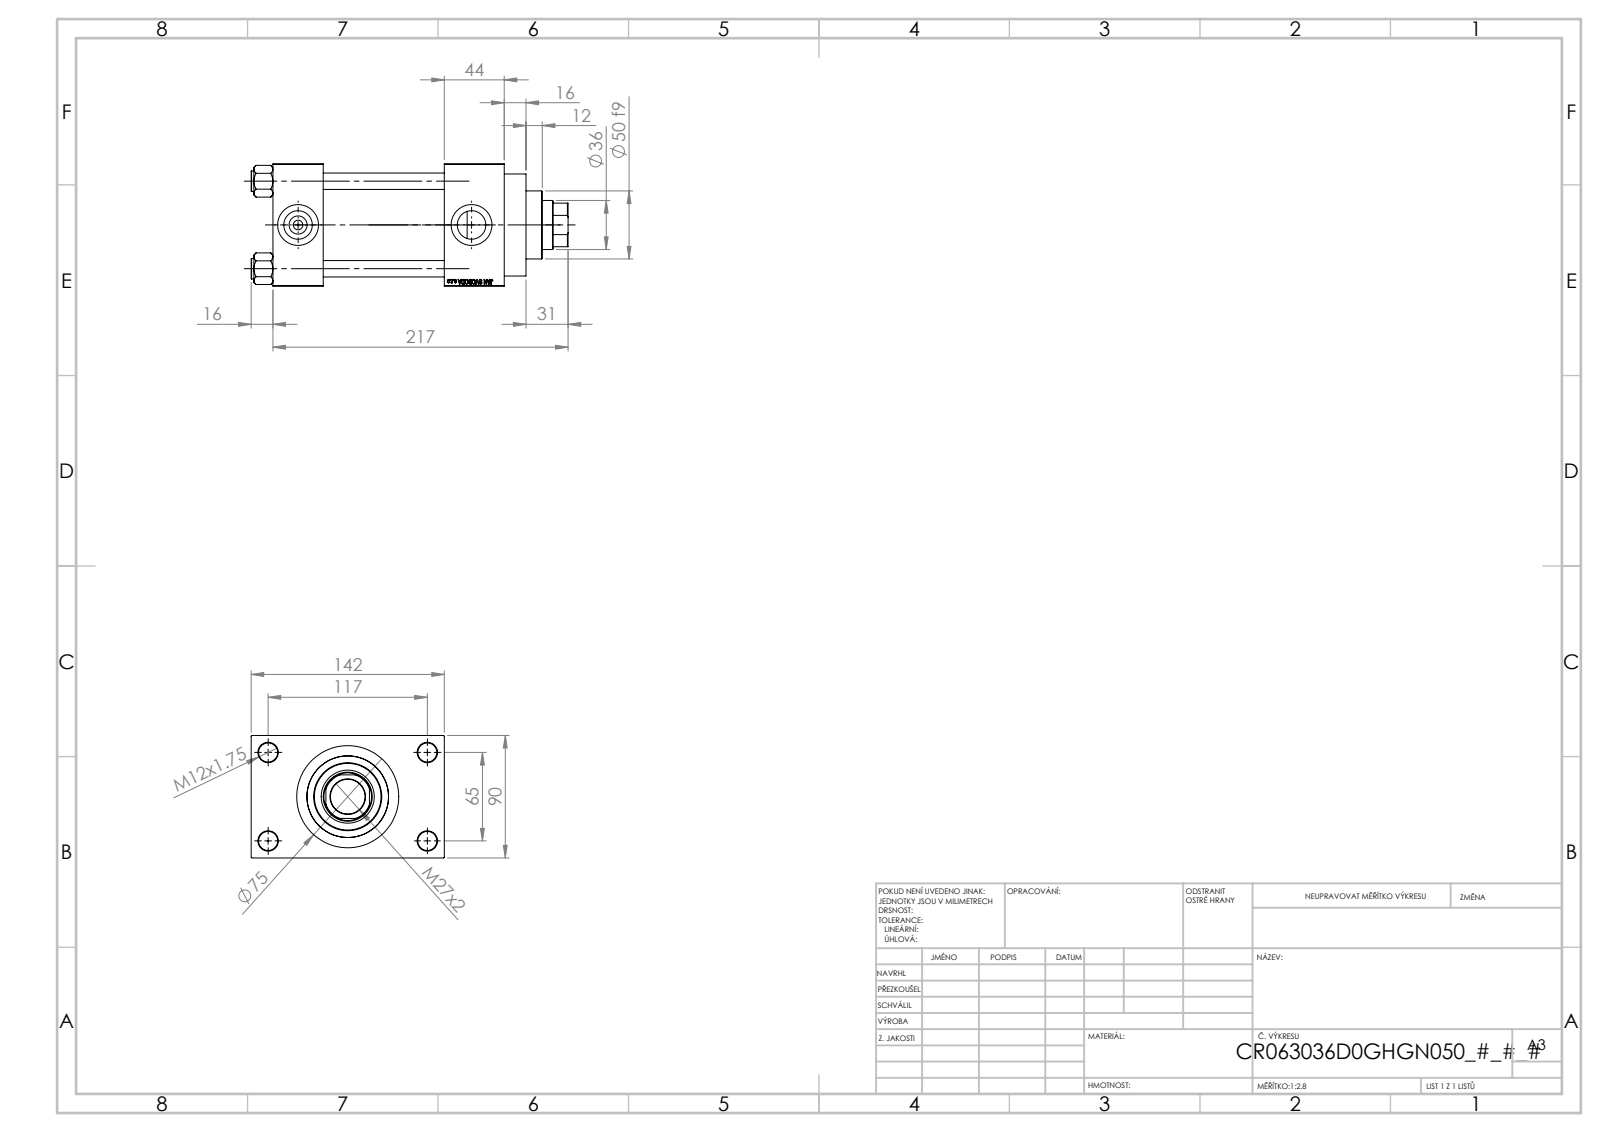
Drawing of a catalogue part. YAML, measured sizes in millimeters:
part_name: "V215CR_VCP_D; NUT_M5_D; V215CR_D_TYCINKA; V215CR_D_Body (+1 more)"
step_written_by: "SolidWorks 2019 (CONFIG_CONTROL_DESIGN)"
units: millimeters
bodies: {solids: 11, faces: 1103, planar: 497, cylindrical: 88, other: 518}
overall_size: [233, 142, 90]
volume: 1174000
surface_area: 226141
round_holes:
  - {diameter: 12, count: 4}
  - {diameter: 14, count: 4}
  - {diameter: 7, count: 2}
  - {diameter: 20.96, count: 2}
  - {diameter: 30, count: 2}
  - {diameter: 25.5, count: 1}
  - {diameter: 36, count: 1}
  - {diameter: 39, count: 1}
  - {diameter: 50, count: 1}
  - {diameter: 60, count: 1}
  - {diameter: 63, count: 1}
round_bosses_or_shafts:
  - {diameter: 15, count: 4}
  - {diameter: 75, count: 1}
  - {diameter: 69, count: 1}
partial_cylinders:
  - {radius: 17.5, count: 1}
face_to_face_distances: [90, 89, 37, 126, 170, 133, 44, 26, 116, 142]
hole_center_spacings: [26.35, 45.47, 64.3, 66.92, 69.81, 90.65, 111.34, 65]
